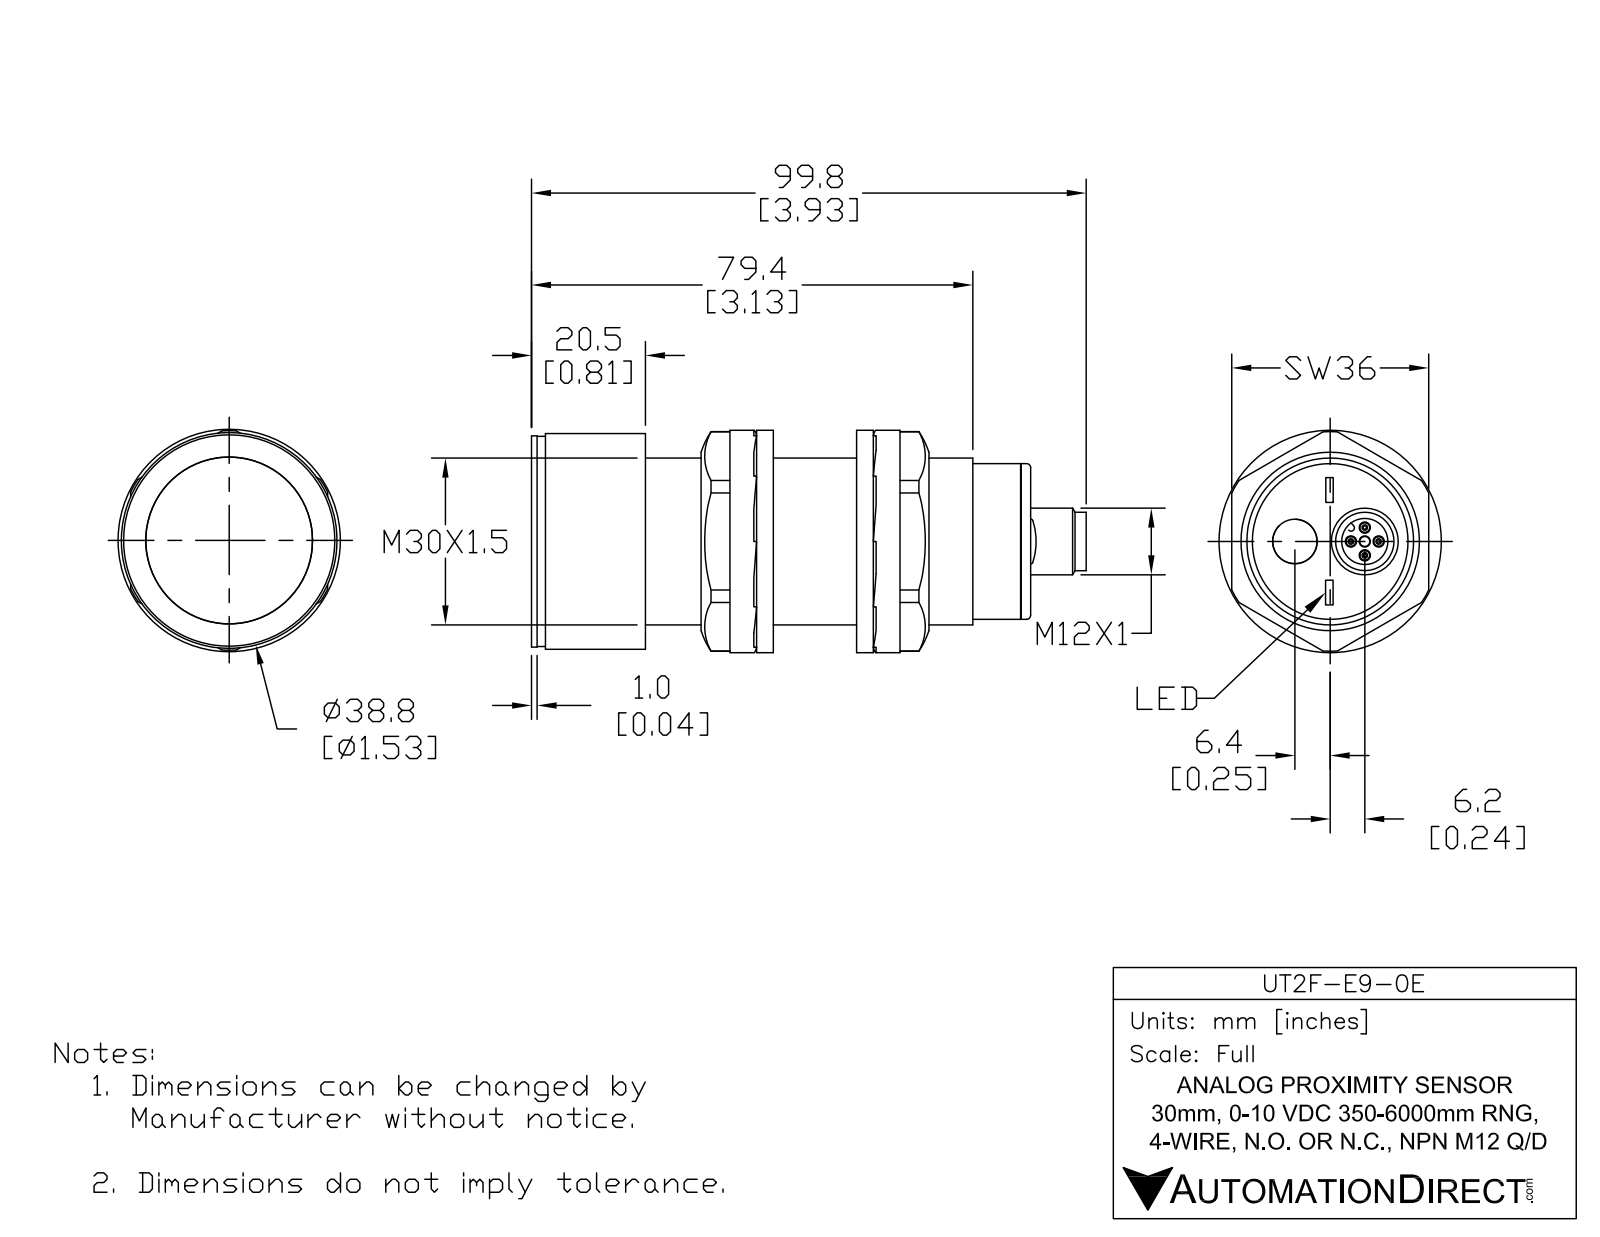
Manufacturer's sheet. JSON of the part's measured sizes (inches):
{"part_name": "UT2F-E9-0E", "step_written_by": "SolidWorks 2017 (AUTOMOTIVE_DESIGN)", "units": "inches", "bodies": {"solids": 5, "faces": 108, "planar": 31, "cylindrical": 47, "other": 30}, "overall_size": [3.894, 1.528, 1.528], "volume_in3": 4.372, "surface_area_in2": 24.88, "round_holes": [[0.071, 4], [0.315, 1], [0.327, 1], [0.372, 1], [1.299, 1]], "round_bosses_or_shafts": [[0.039, 4], [1.528, 1], [1.488, 1], [1.181, 1], [1.102, 1], [0.472, 1], [0.413, 1], [0.364, 1]], "partial_cylinders_radius": [[0.012, 2], [0.024, 1]], "face_to_face_distances": [3.37, 0.059, 3.429, 0.767, 0.709, 2.661, 0.059, 3.429, 0.071, 3.5], "hole_center_spacings": [0.098, 0.139, 0.197, 0.264, 0.505, 0.146, 0.245, 0.25]}
